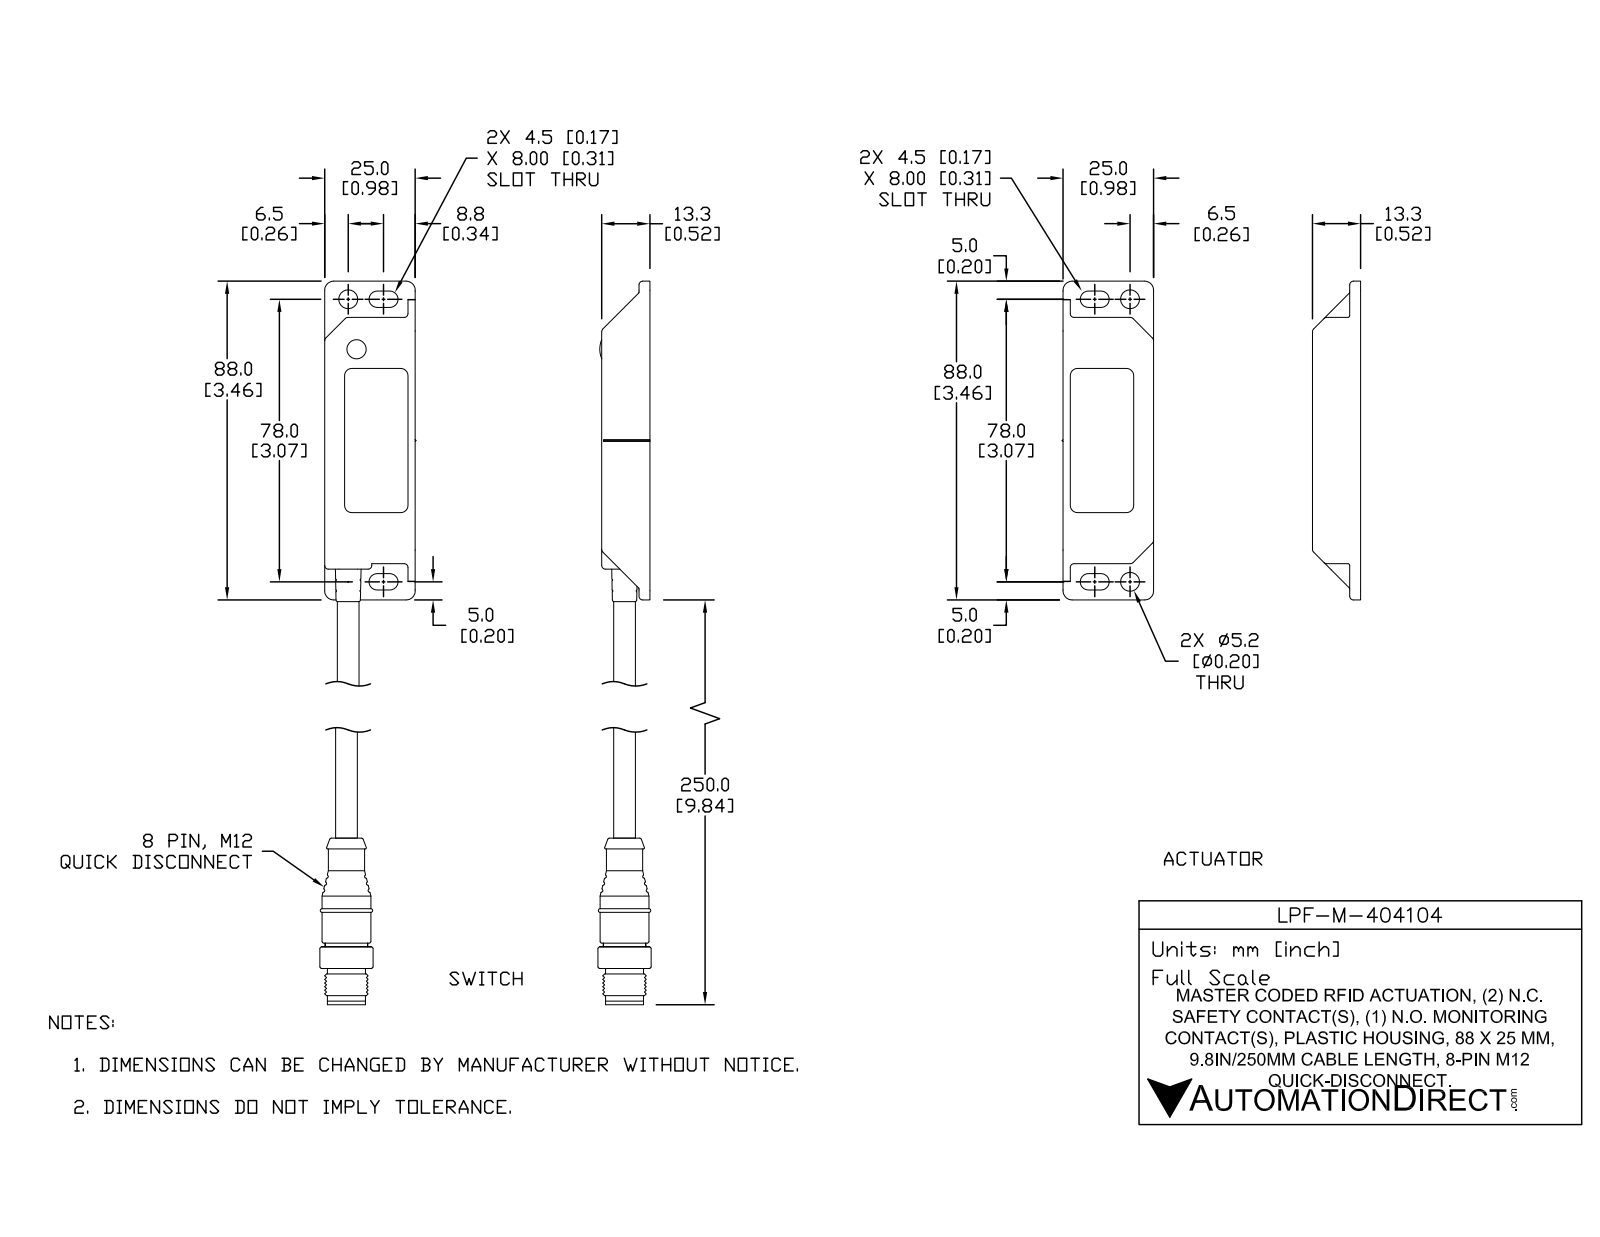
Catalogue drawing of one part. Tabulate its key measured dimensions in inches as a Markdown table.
| quantity | value |
| --- | --- |
| part name | LPF-M-404104; LPF-M-404104_2; LPF-M-404104_1 |
| STEP written by | SolidWorks 2017 (AUTOMOTIVE_DESIGN) |
| units | inches |
| bodies | 12 solids, 1419 faces (558 planar, 417 cylindrical, 444 other) |
| overall size | 12.972 × 2.026 × 0.579 |
| volume | 2.034 in³ |
| surface area | 54.51 in² |
| round holes (diameter × count) | 0.197 × 4, 0.205 × 4, 0.119 × 1, 0.173 × 1, 0.213 × 1, 0.232 × 1, 0.276 × 1, 0.327 × 1, 0.465 × 1 |
| round bosses / shafts (diameter × count) | 0.031 × 8, 0.079 × 4, 0.193 × 2, 0.091 × 2, 0.531 × 1, 0.461 × 1, 0.413 × 1, 0.394 × 1 |
| partial cylindrical surfaces (radius × count) | 0.02 × 116, 0.039 × 49, 0.079 × 10, 0.089 × 8, 0.098 × 8, 0.012 × 6, 0.189 × 1, 0.289 × 1 |
| main face-to-face distances | 0.067, 0.441, 0.079, 0.374, 0.059, 0.071, 0.508, 0.445, 0.512, 0.988 |
| hole center spacings | 0.748, 1.097, 1.19, 1.275, 1.48, 1.571, 1.784, 1.895 |
